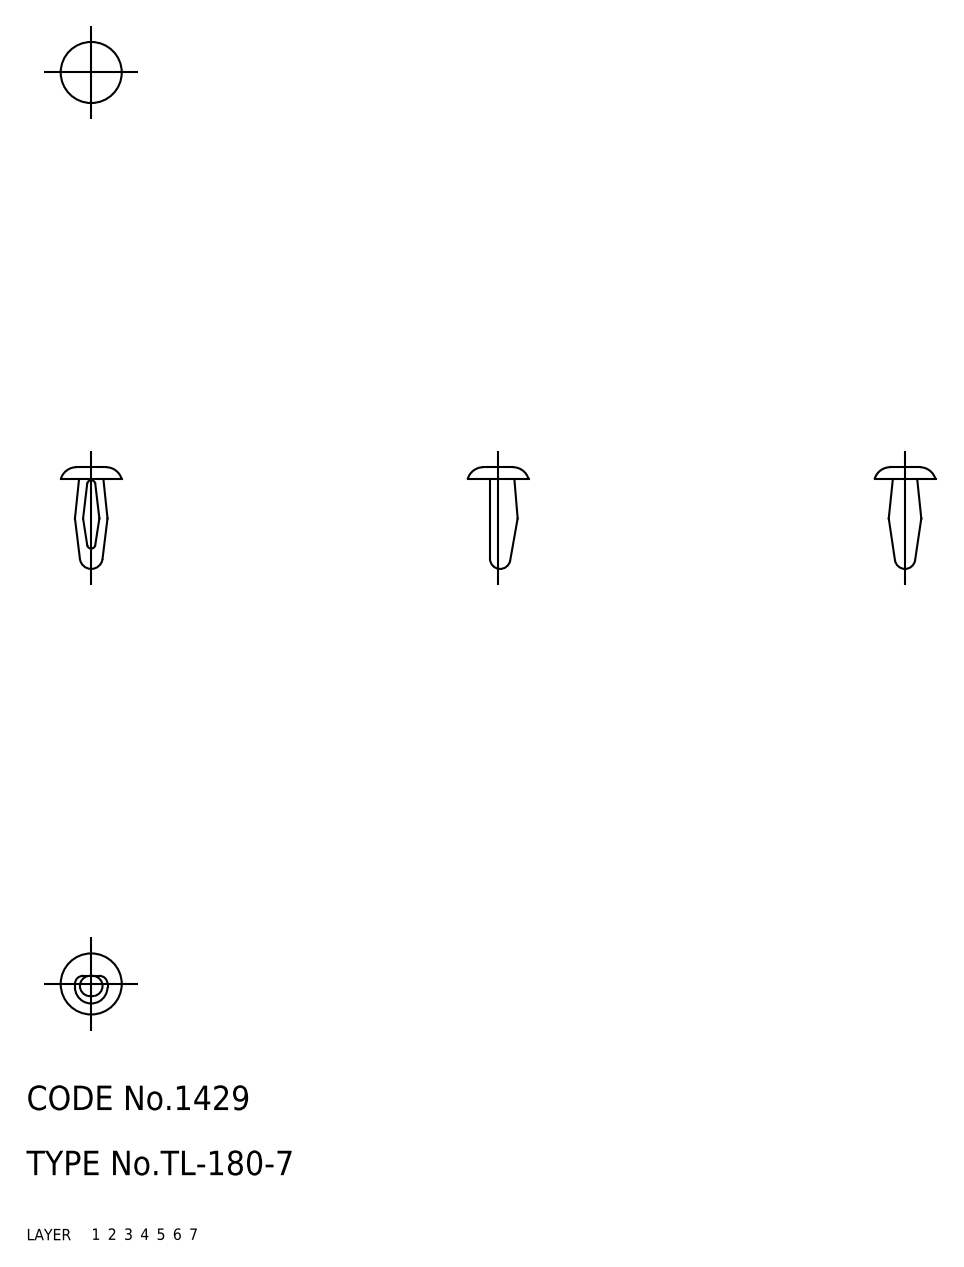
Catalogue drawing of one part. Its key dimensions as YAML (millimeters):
part_name: "fastener"
step_written_by: "CADfix (AUTOMOTIVE_DESIGN)"
units: millimeters
bodies: {solids: 1, faces: 34, planar: 0, cylindrical: 0, other: 34}
overall_size: [12.5, 7.5, 7.5]
volume: 127
surface_area: 239
